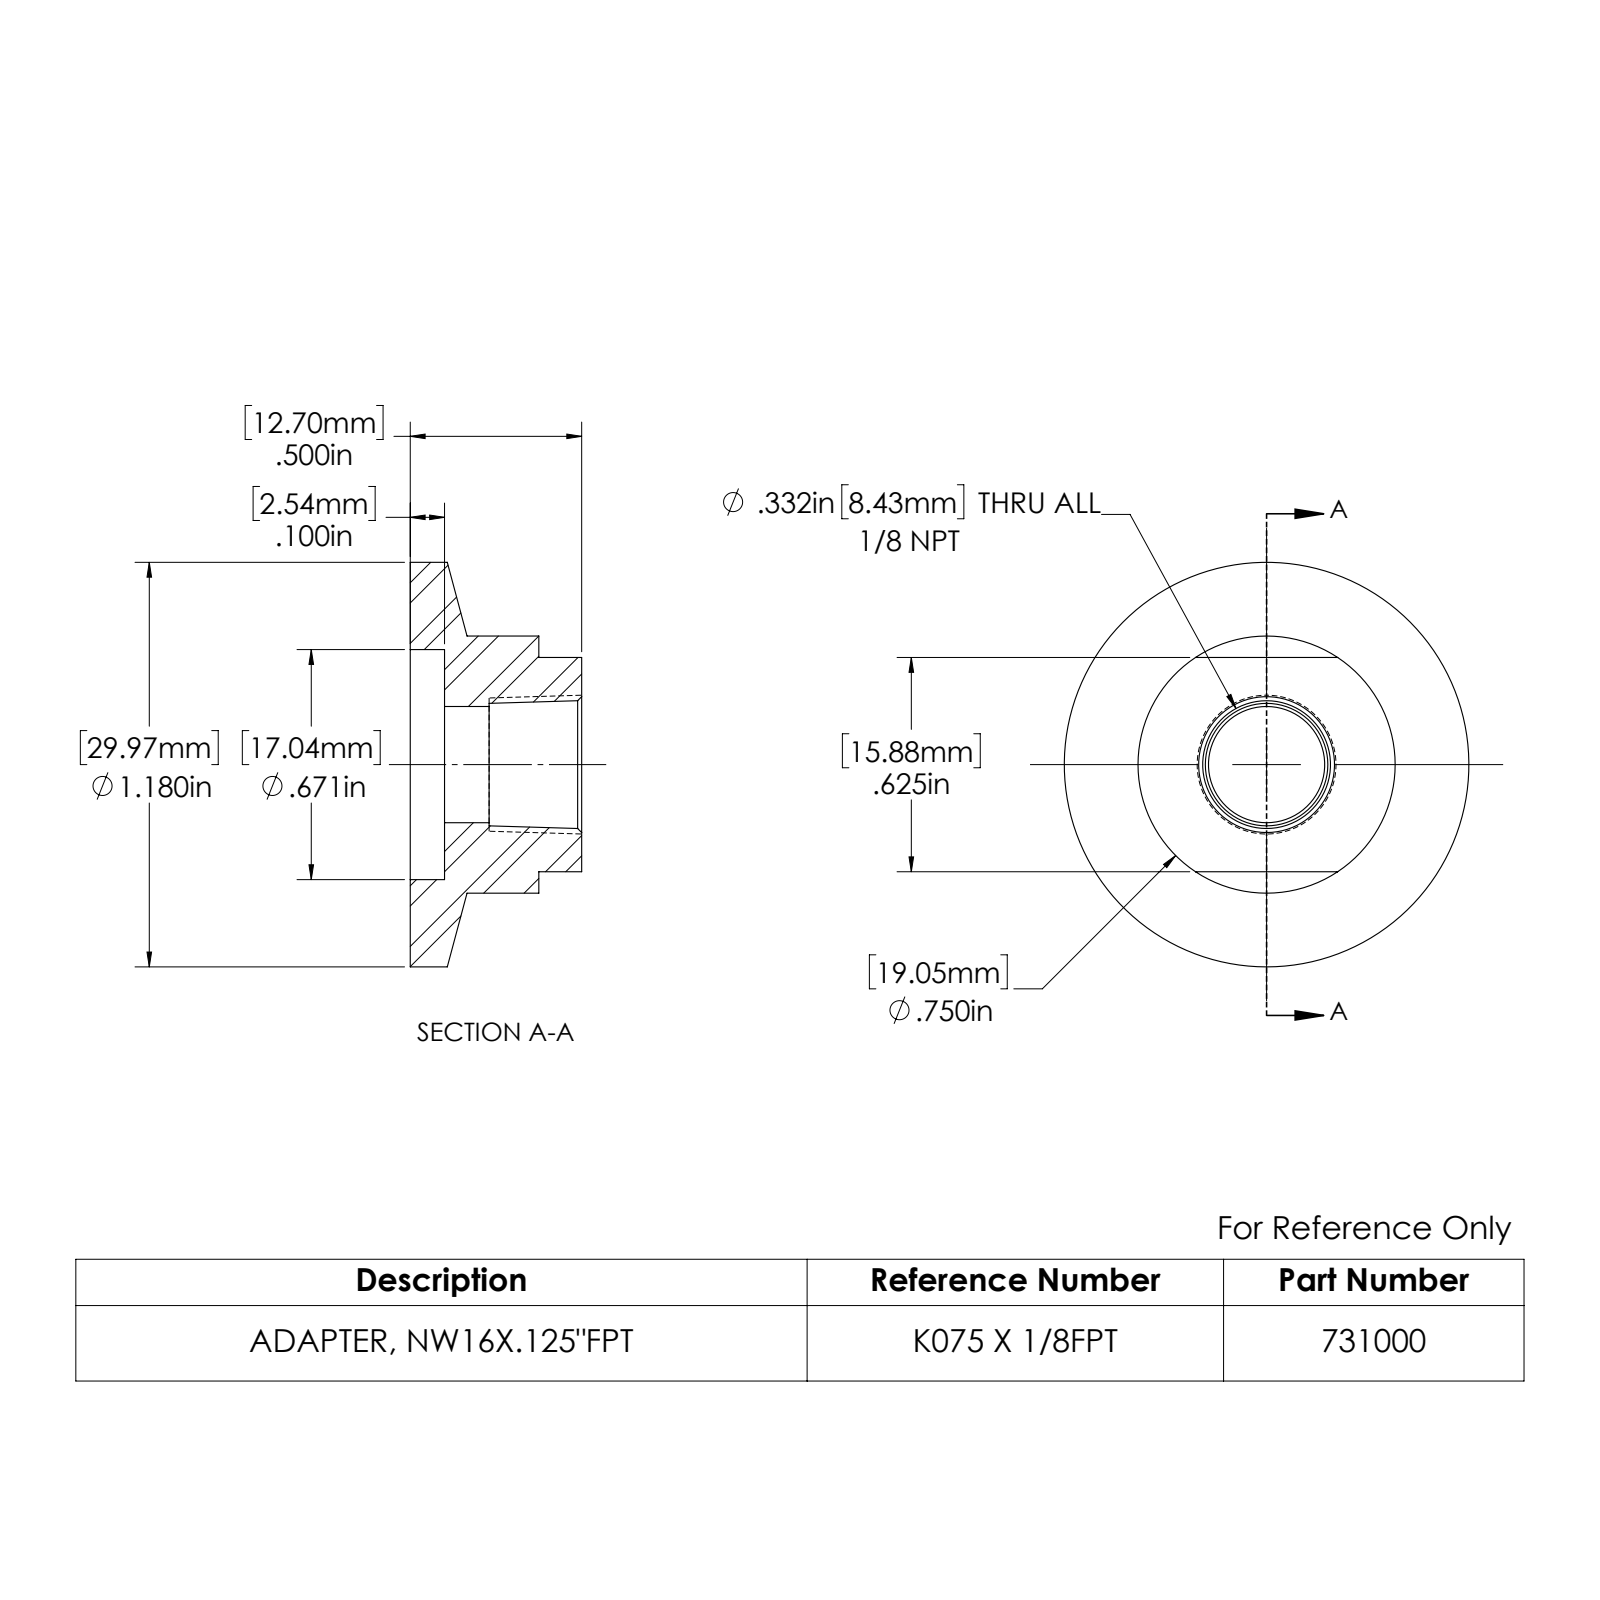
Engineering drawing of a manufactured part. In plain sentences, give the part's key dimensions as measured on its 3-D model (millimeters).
The part is named "731000". Its 3-D file was written by "SolidWorks 2022 (AUTOMOTIVE_DESIGN)". It is 1 solid with 17 faces: 7 planar, 8 cylindrical and 2 other. Overall it measures 30 by 30 by 12.7 millimeters. Its volume is 3 750 cubic millimeters and its surface area 2 485 square millimeters. Round holes: 1 of diameter 9.1, 1 of diameter 17. Round bosses or shafts: 1 of diameter 30, 1 of diameter 19.1. The main face-to-face distances are 12.7, 10.2, 2.5, 15.9, 3.2, 7, 9.5.
